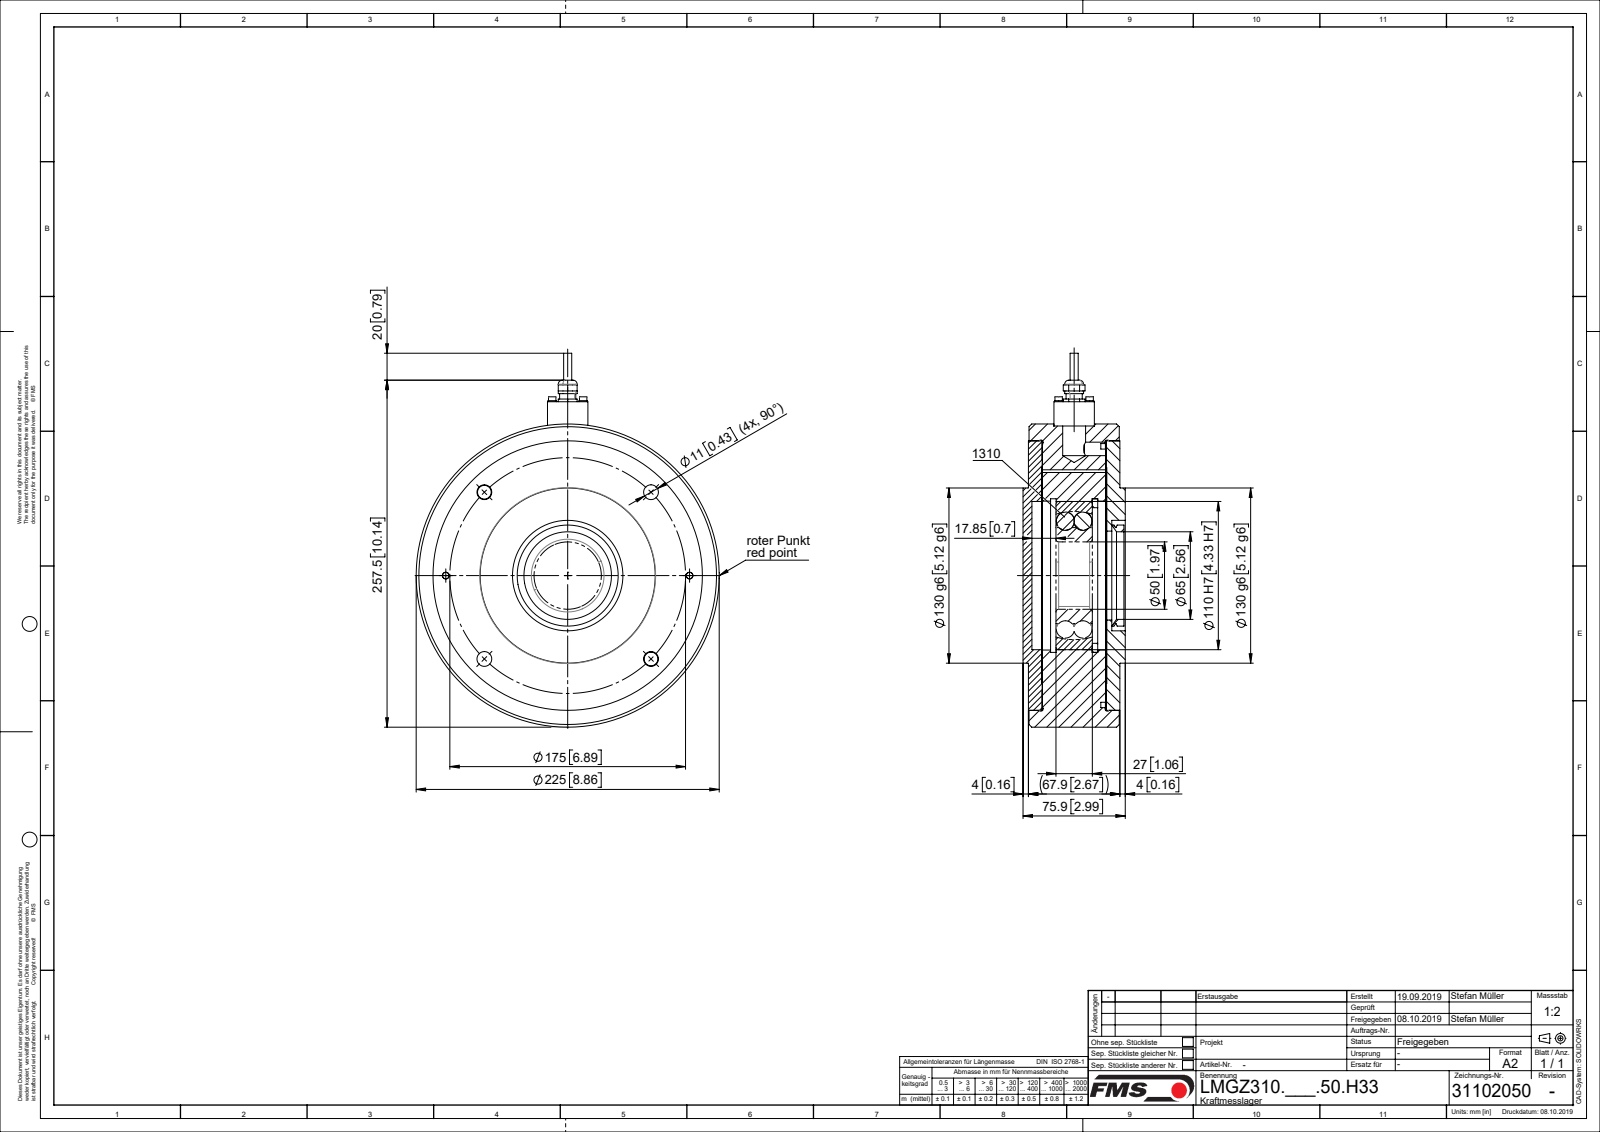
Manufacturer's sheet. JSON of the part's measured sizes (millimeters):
{"part_name": "ZEICHNUNG9; L50007; L4765504; TEIL1 (+8 more)", "step_written_by": "Mechanical Desktop 2009 (CONFIG_CONTROL_DESIGN)", "units": "millimeters", "bodies": {"solids": 20, "faces": 369, "planar": 113, "cylindrical": 200, "other": 56}, "overall_size": [257.5, 225, 75.9], "volume_mm3": 2384000, "surface_area_mm2": 384737, "round_holes": [[11, 6], [2.6, 4], [3.2, 4], [3.4, 4], [9, 4], [5, 2], [6.6, 2], [6, 1], [11.28, 1], [23, 1], [50, 1], [64, 1]], "round_bosses_or_shafts": [[6.2, 4], [5.5, 4], [3, 4], [10, 2], [6, 2], [225, 1], [199, 1], [130, 1]], "partial_cylinders_radius": [[81, 1], [86, 1]], "face_to_face_distances": [9.7, 47.25, 10.45, 10.75, 47.45, 10.2, 57.45, 57.7, 47, 10], "hole_center_spacings": [16.26, 23, 68.17, 87.5, 123.74, 164.45, 32.53, 90.5]}
